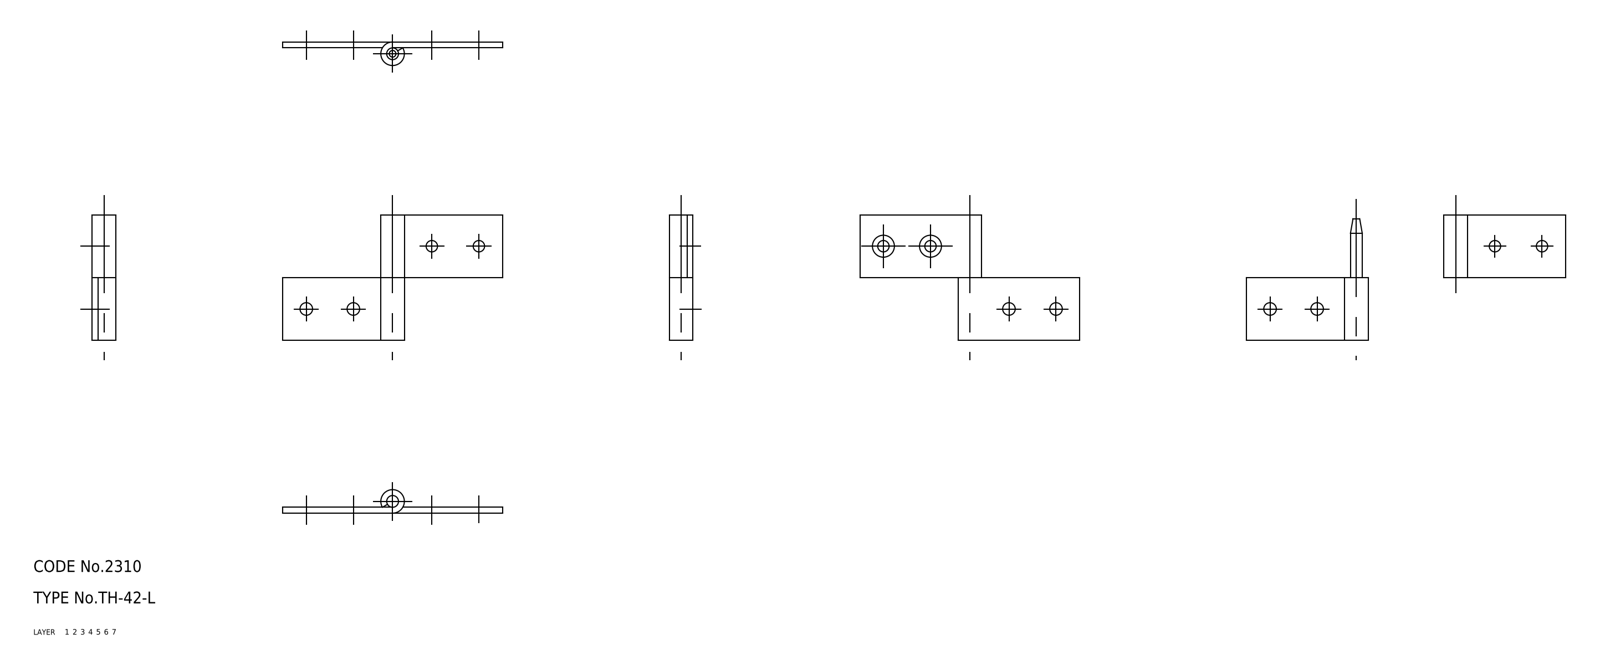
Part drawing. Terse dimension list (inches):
name: shaft; hinge piece_B; hinge piece_A; TH_42_L_9042_36
written by: CADfix (AUTOMOTIVE_DESIGN)
unit: in
bodies: 3 solids, 34 faces (0 planar, 0 cylindrical, 34 other)
size: 2.205 × 1.26 × 0.236
volume: 0.125 in³; area: 4.9 in²
